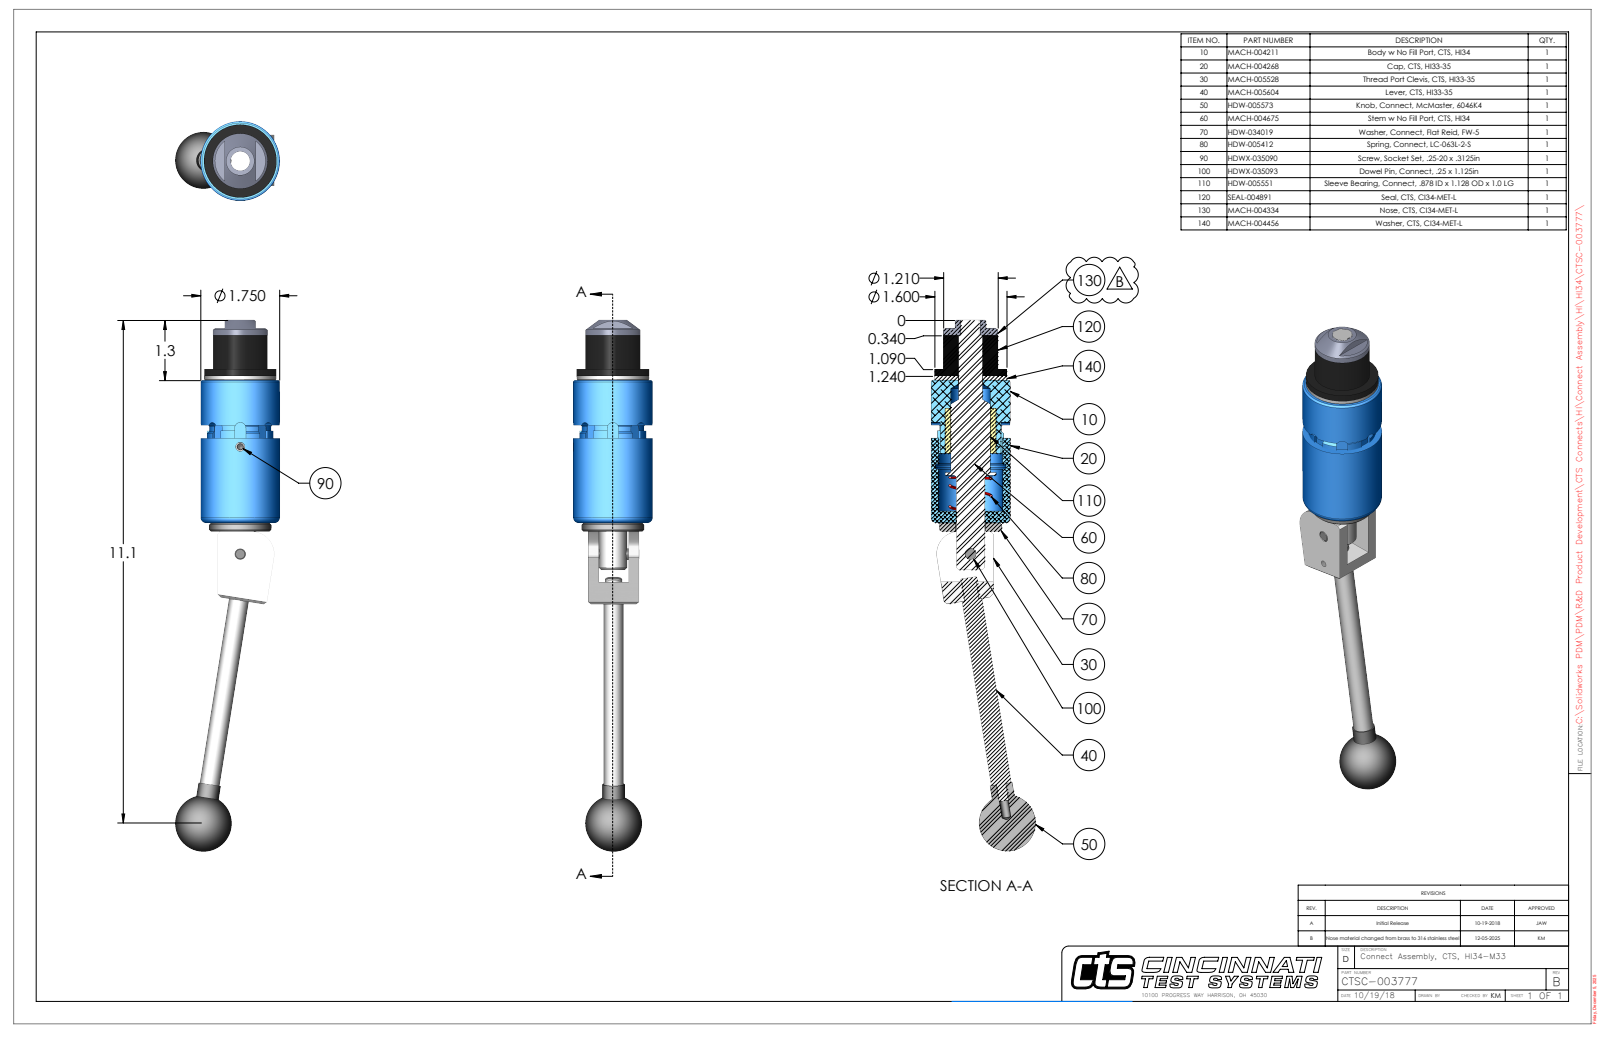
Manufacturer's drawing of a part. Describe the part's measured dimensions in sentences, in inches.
The part is named "CTSC-003777". Its 3-D file was written by "SolidWorks 2023 (AUTOMOTIVE_DESIGN)". It is 9 solids with 271 faces: 101 planar, 113 cylindrical and 57 other. Overall it measures 11.77 by 2.312 by 1.75 inches. Its volume is 12.32 cubic inches and its surface area 72.97 square inches. Round holes: 2 of diameter 0.201, 1 of diameter 0.15, 1 of diameter 0.249, 1 of diameter 0.251, 1 of diameter 0.313, 1 of diameter 0.422, 1 of diameter 0.53, 1 of diameter 0.541, 1 of diameter 0.547, 1 of diameter 0.635, 1 of diameter 0.656. Round bosses or shafts: 2 of diameter 0.5, 2 of diameter 0.44, 2 of diameter 0.25, 1 of diameter 1.75, 1 of diameter 1.6, 1 of diameter 1.38, 1 of diameter 1.21, 1 of diameter 0.625. Partial cylindrical surfaces (rounded edges, fillets, slot ends): 4 of radius 0.125, 2 of radius 0.029, 1 of radius 0.5, 1 of radius 0.695, 1 of radius 0.709, 1 of radius 0.744, 1 of radius 0.816. The main face-to-face distances are 0.094, 3.255, 3.161, 0.9, 0.994, 4.155, 1.12, 4.343, 3.443, 3.349. The hole center spacings are 0.74, 2.376, 3.116.
